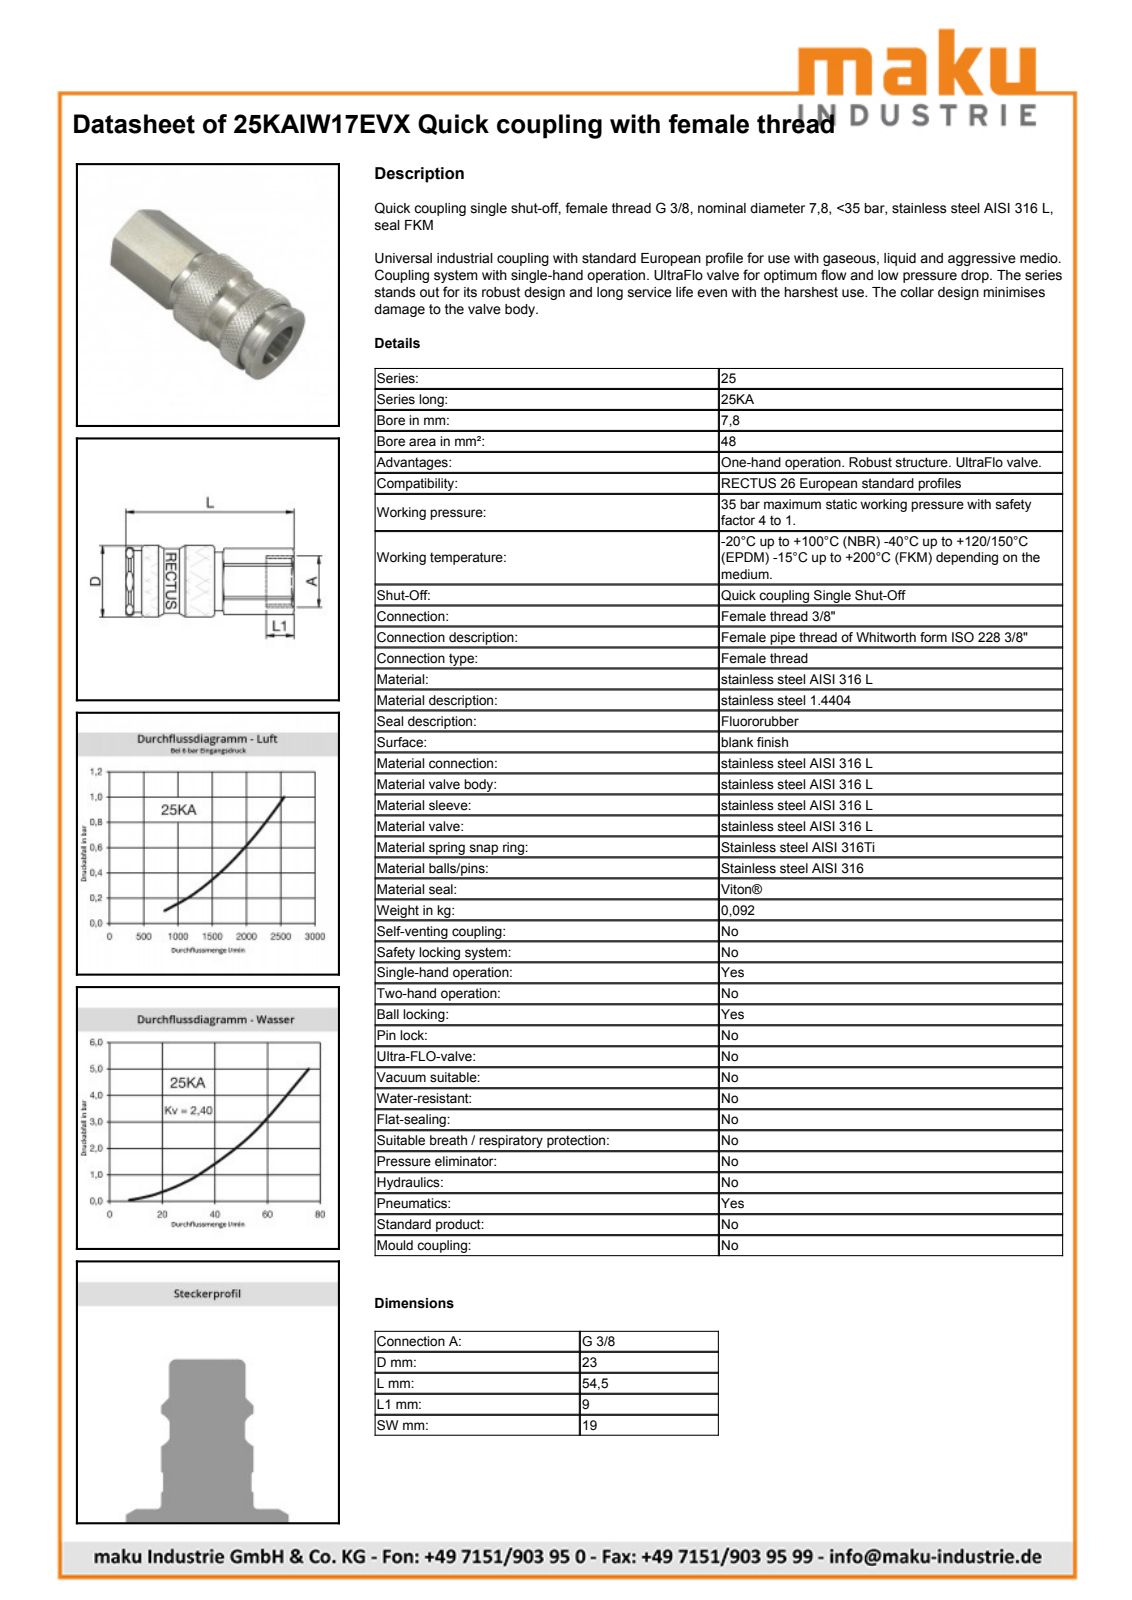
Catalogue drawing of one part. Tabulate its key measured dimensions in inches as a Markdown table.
| quantity | value |
| --- | --- |
| part name | D106030 |
| STEP written by | Autodesk Inventor 2011 (AUTOMOTIVE_DESIGN) |
| units | inches |
| bodies | 2 solids, 604 faces (238 planar, 83 cylindrical, 283 other) |
| overall size | 2.146 × 0.911 × 0.911 |
| volume | 1.002 in³ |
| surface area | 13.1 in² |
| round holes (diameter × count) | 0.555 × 1, 0.589 × 1, 0.594 × 1, 0.63 × 1, 0.677 × 1, 0.679 × 1, 0.762 × 1, 0.789 × 1 |
| round bosses / shafts (diameter × count) | 0.911 × 1, 0.866 × 1, 0.827 × 1, 0.787 × 1, 0.746 × 1, 0.602 × 1, 0.551 × 1 |
| partial cylindrical surfaces (radius × count) | 0.265 × 1, 0.409 × 1, 0.421 × 1 |
| main face-to-face distances | 0.748, 1.874, 0.207, 0.758, 2.146, 0.272, 1.132, 0.742, 1.014, 0.098 |
